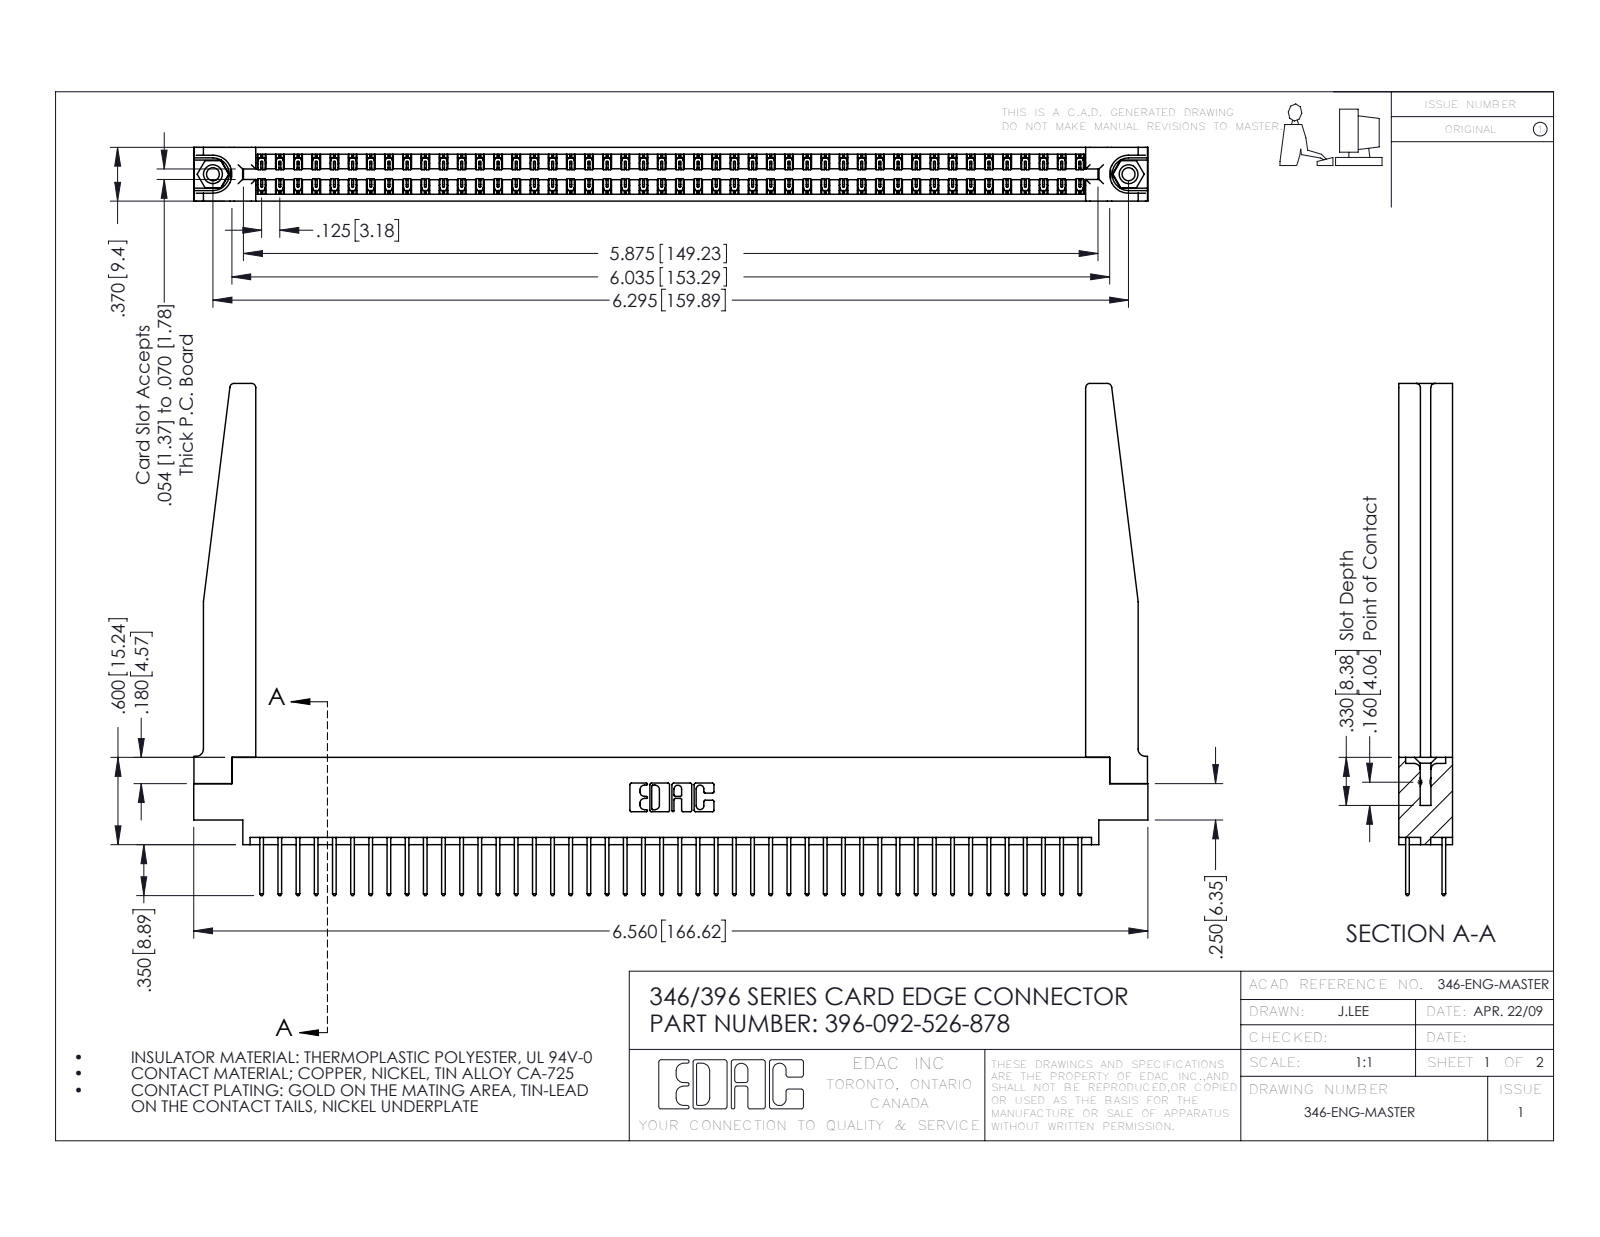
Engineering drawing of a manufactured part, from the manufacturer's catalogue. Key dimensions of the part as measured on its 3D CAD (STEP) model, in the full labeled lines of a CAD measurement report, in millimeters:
Part name (STEP PRODUCT): 396-092-526-878; 345-250-001_345-250-001-102; 346 Part_0.170 Offset - 0.156 Dia-TH; 345-292-001_345-293-126 (+1 more)
STEP written by: SolidWorks 2016 (CONFIG_CONTROL_DESIGN)
Units: millimetres
Bodies: 97 solids, 5144 faces (3442 planar, 1650 cylindrical, 52 other)
Overall size (bounding box): 166.6 × 89.4 × 9.4
Volume: 23 190 mm³ · Surface area: 29 830 mm²
Round holes (diameter × count): ⌀2.3 ×2, ⌀3.2 ×2, ⌀4 ×2, ⌀1.6 ×1
Round bosses / shafts (diameter × count): ⌀3.9 ×2
Partial cylindrical surfaces — rounded edges, fillets, slot ends (radius × count): R0.2 ×138, R0.3 ×92, R0.3 ×22, R0.8 ×8, R0.2 ×6, R0.8 ×6, R0.7 ×3, R0.4 ×2
Main face-to-face distances: 1.2, 8.2, 9.4, 1.8, 6.4, 7.6, 0.6, 3.8, 3.8, 7
Hole centre spacings: 6.2, 154.6, 159.9
